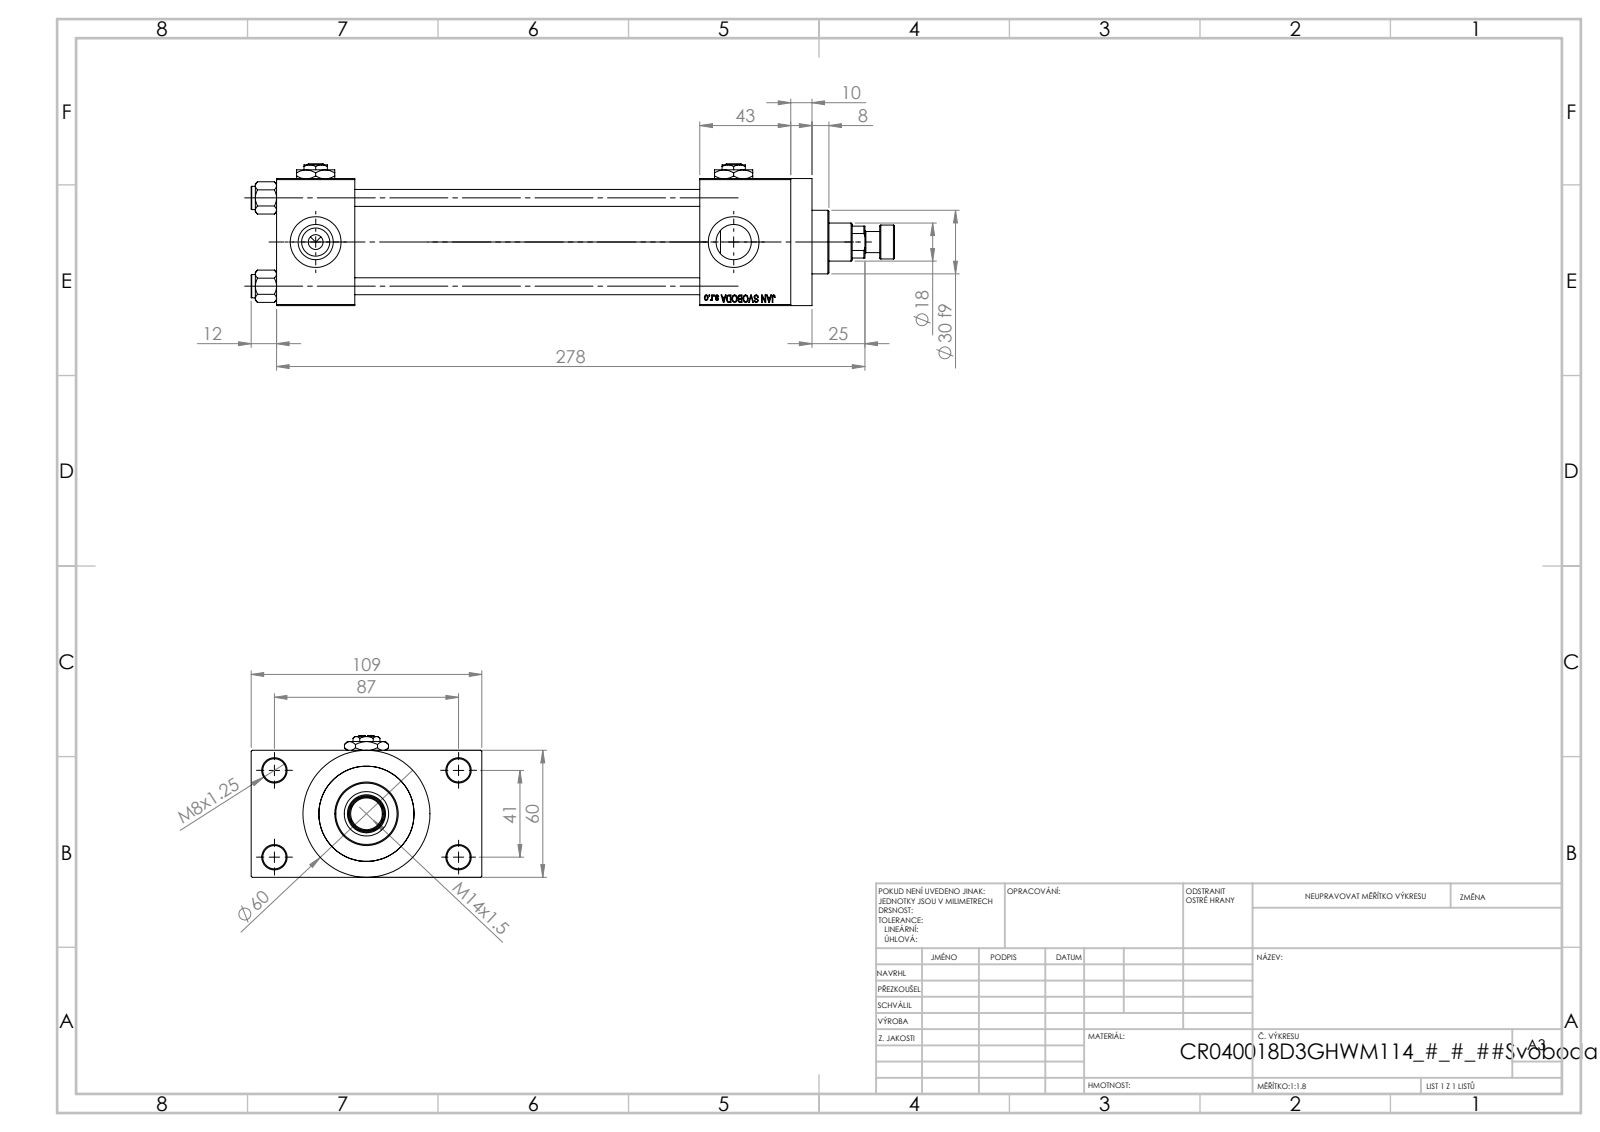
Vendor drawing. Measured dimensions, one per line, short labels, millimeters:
name: V215_VC_A; V215CR_D_Body; NUT_M5_D; V215CR_VCP_D (+3 more)
written by: SolidWorks 2019 (CONFIG_CONTROL_DESIGN)
unit: mm
bodies: 14 solids, 1218 faces (549 planar, 103 cylindrical, 566 other)
size: 304 × 109 × 67
volume: 602 677 mm³; area: 171 030 mm²
holes: 4× ⌀8, 4× ⌀11, 4× ⌀16.66, 4× ⌀24, 3× ⌀7, 1× ⌀8.5, 1× ⌀18, 1× ⌀21, 1× ⌀31, 1× ⌀40, 1× ⌀45
bosses: 4× ⌀11, 1× ⌀60, 1× ⌀46, 1× ⌀30, 1× ⌀16, 1× ⌀10
rounds: 1× R8.5
face distances: 60, 24.5, 163, 84.5, 37, 200, 43, 243, 206, 10
hole spacings: 22.65, 29.49, 41.7, 47.15, 48.09, 64.35, 76.49, 41
